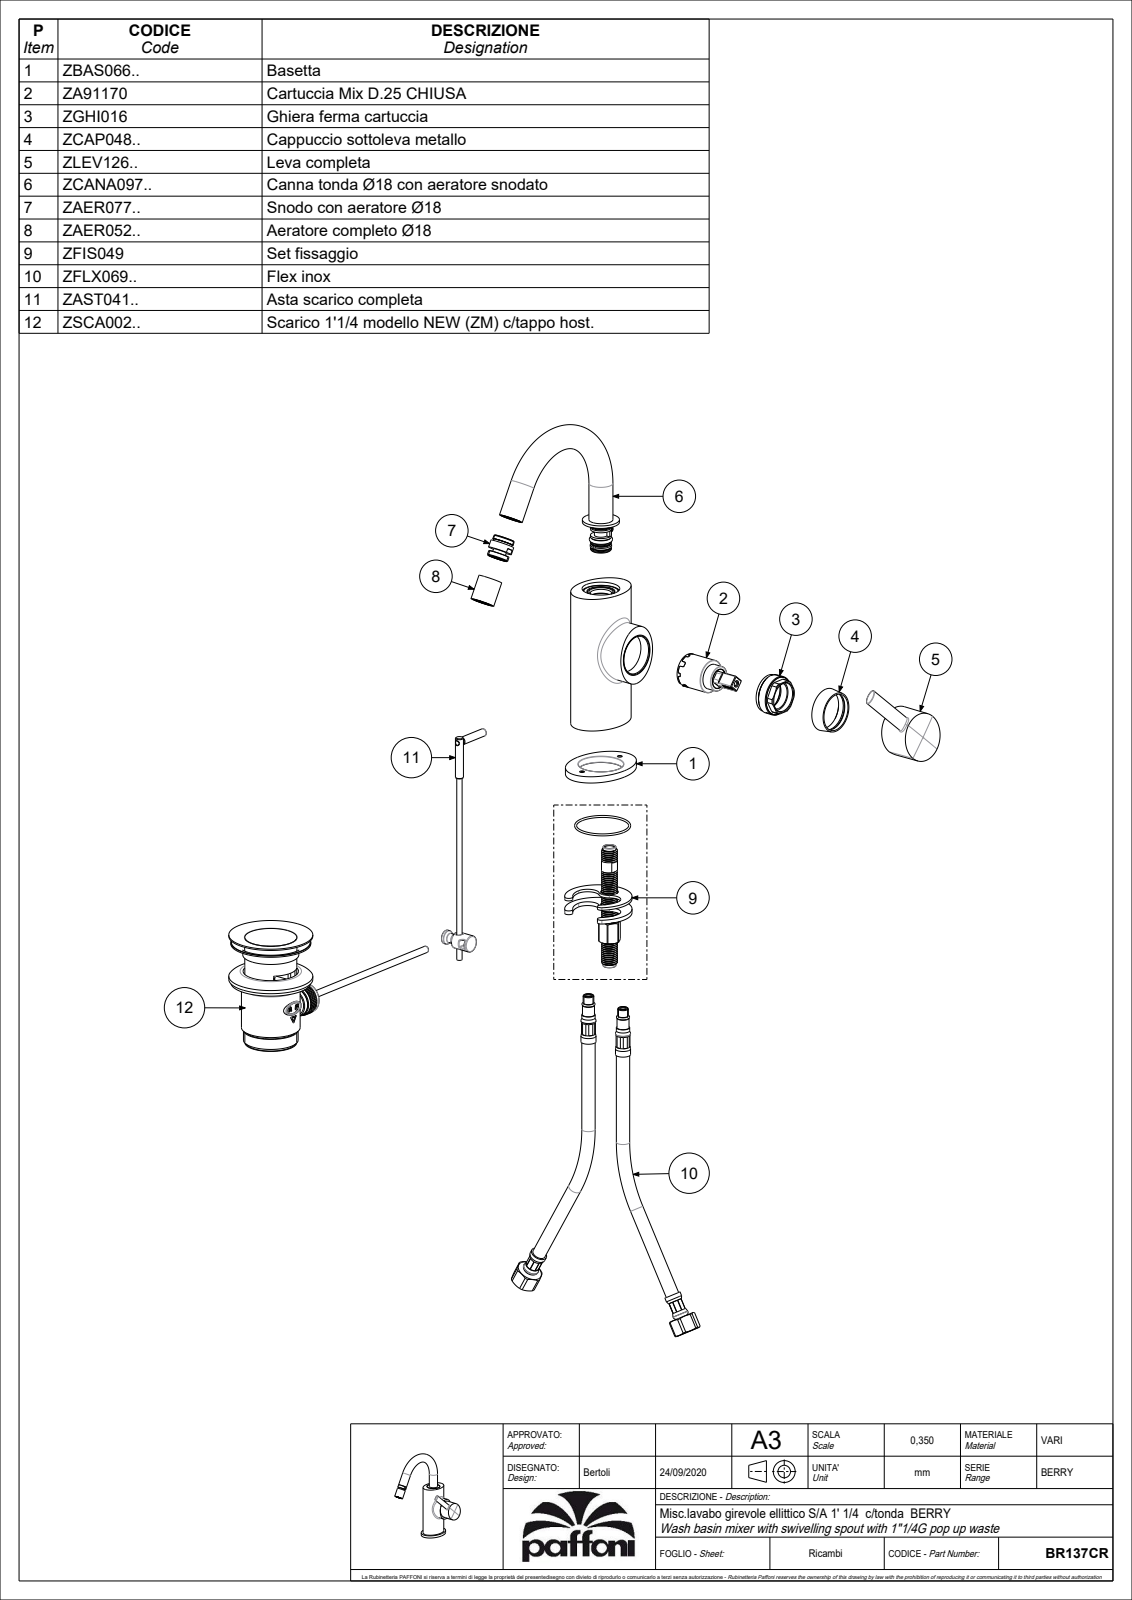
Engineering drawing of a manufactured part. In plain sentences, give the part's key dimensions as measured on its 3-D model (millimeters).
The part is named "BR137CR". Its 3-D file was written by "CREO PARAMETRIC BY PTC INC, 2020044 (CONFIG_CONTROL_DESIGN)". It is 4 solids with 1507 faces: 612 planar, 579 cylindrical and 316 other. Overall it measures 197.09 by 164.14 by 83.2 millimeters. Its volume is 215 039 cubic millimeters and its surface area 81 701 square millimeters. Round holes: 51 of diameter 0.5, 4 of diameter 5, 4 of diameter 6, 2 of diameter 3, 2 of diameter 4, 2 of diameter 4.5, 2 of diameter 5.5, 2 of diameter 9.4, 2 of diameter 13, 2 of diameter 14, 2 of diameter 15, 1 of diameter 3.3. Round bosses or shafts: 3 of diameter 10, 3 of diameter 9, 2 of diameter 18, 2 of diameter 12, 2 of diameter 4, 1 of diameter 38.8, 1 of diameter 28.5, 1 of diameter 27.8. Partial cylindrical surfaces (rounded edges, fillets, slot ends): 40 of radius 0.5, 17 of radius 0.3, 15 of radius 1, 13 of radius 0.2, 10 of radius 0.15, 10 of radius 2, 4 of radius 1.25, 4 of radius 2.45. The main face-to-face distances are 110, 8, 3, 5, 2, 7, 105, 1.9, 102, 0.5. The hole center spacings are 1.5, 3.35, 2.12, 5.41, 3, 4.74, 6.71, 3.36.
